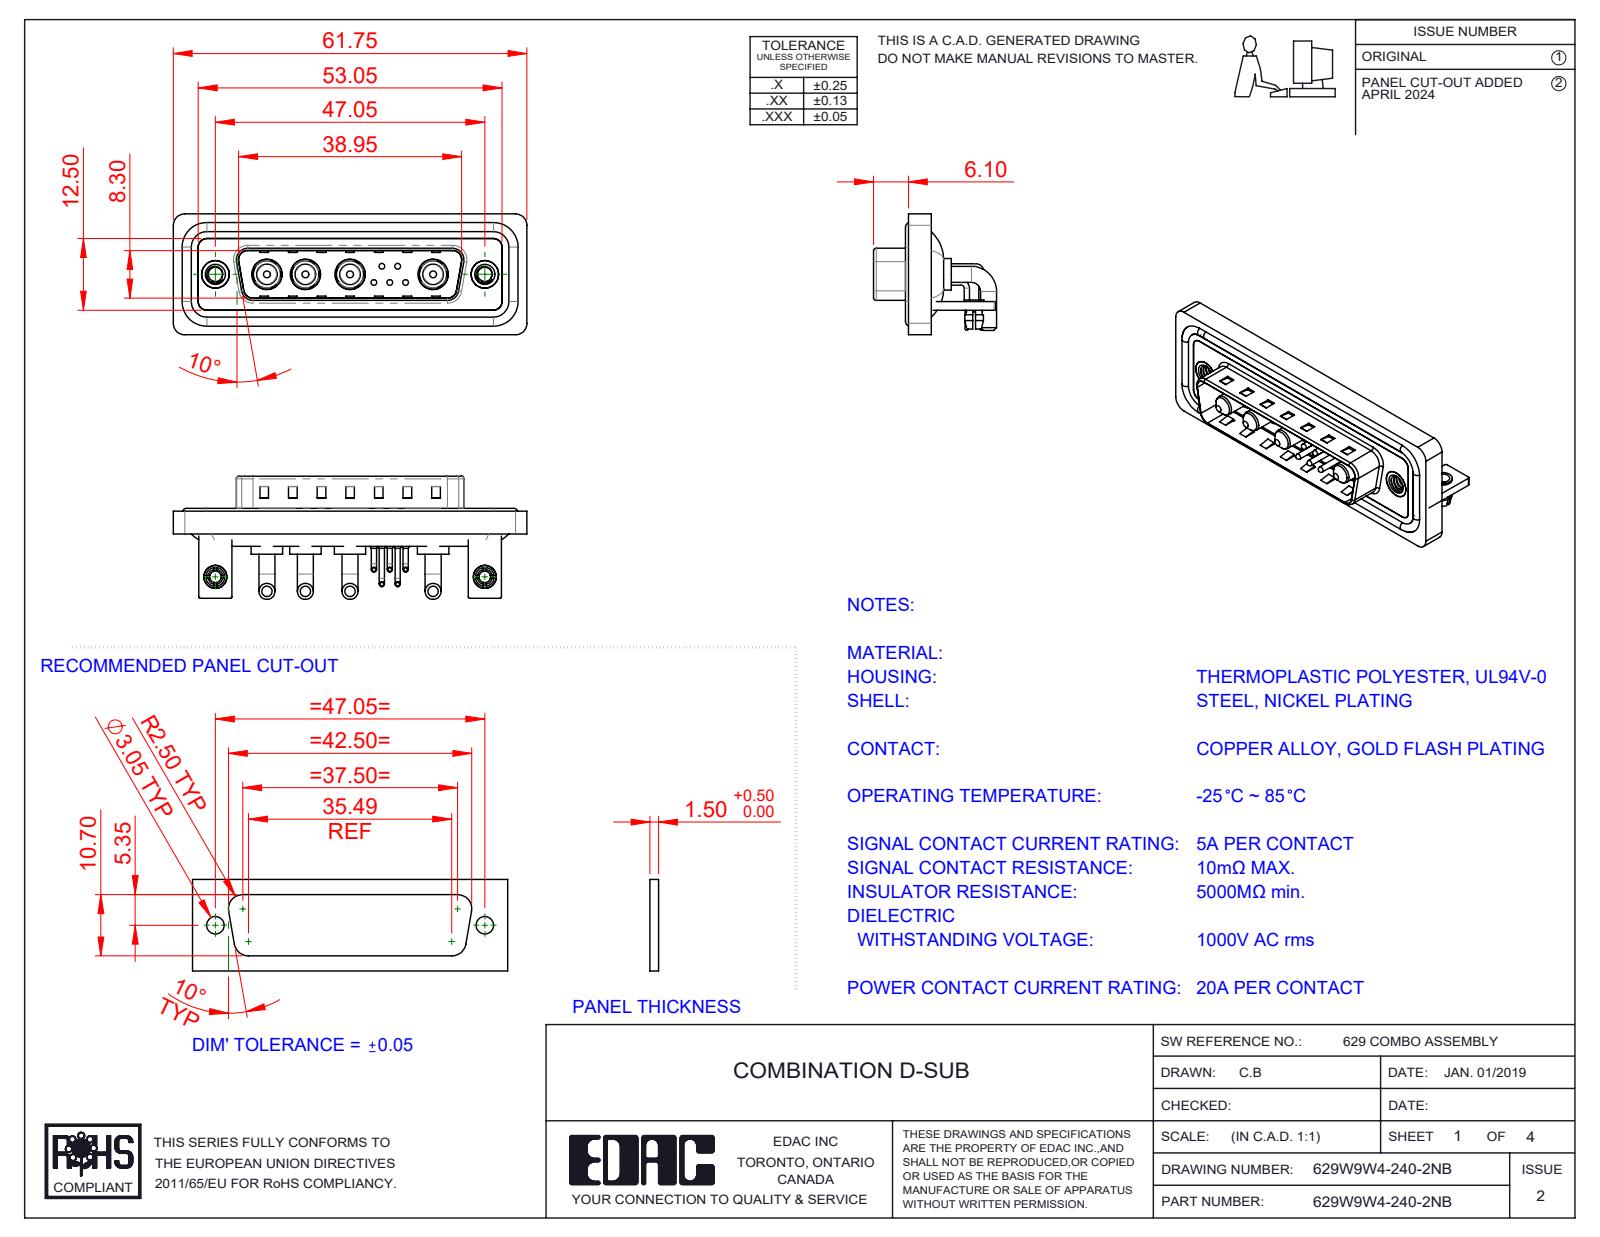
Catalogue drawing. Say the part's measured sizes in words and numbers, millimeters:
The part is named "629Combo Waterproof Housing_25 Contacts; 629Combo Contact Row 2; 629Combo Threaded Rivet_B; 629W9W4-240-2NB (+7 more)". Its 3-D file was written by "SolidWorks 2023 (CONFIG_CONTROL_DESIGN)". It is 24 solids with 1335 faces: 637 planar, 502 cylindrical and 196 other. Overall it measures 61.75 by 21.5 by 21.1 millimeters. Its volume is 8 012 cubic millimeters and its surface area 13 175 square millimeters. Round holes: 7 of diameter 2, 5 of diameter 0.75, 5 of diameter 1.6, 4 of diameter 2.5, 4 of diameter 4.85, 4 of diameter 5.3, 2 of diameter 3.2, 2 of diameter 4, 2 of diameter 4.8, 2 of diameter 5. Round bosses or shafts: 10 of diameter 0.9, 8 of diameter 2.8, 5 of diameter 1.5, 5 of diameter 1, 5 of diameter 0.65, 4 of diameter 5.5, 4 of diameter 5.2, 4 of diameter 4.75. Partial cylindrical surfaces (rounded edges, fillets, slot ends): 19 of radius 2, 18 of radius 1.5, 16 of radius 0.25, 9 of radius 0.5, 8 of radius 1.6, 5 of radius 1.01, 4 of radius 0.6, 4 of radius 0.65. The main face-to-face distances are 0.4, 1.5, 0.8, 2.9, 2.1, 1.1, 3.7, 4.1, 4.5, 1.6. The hole center spacings are 3.16, 2.77, 5.04, 14.5, 47.05, 2.78, 4.4, 4.41.
